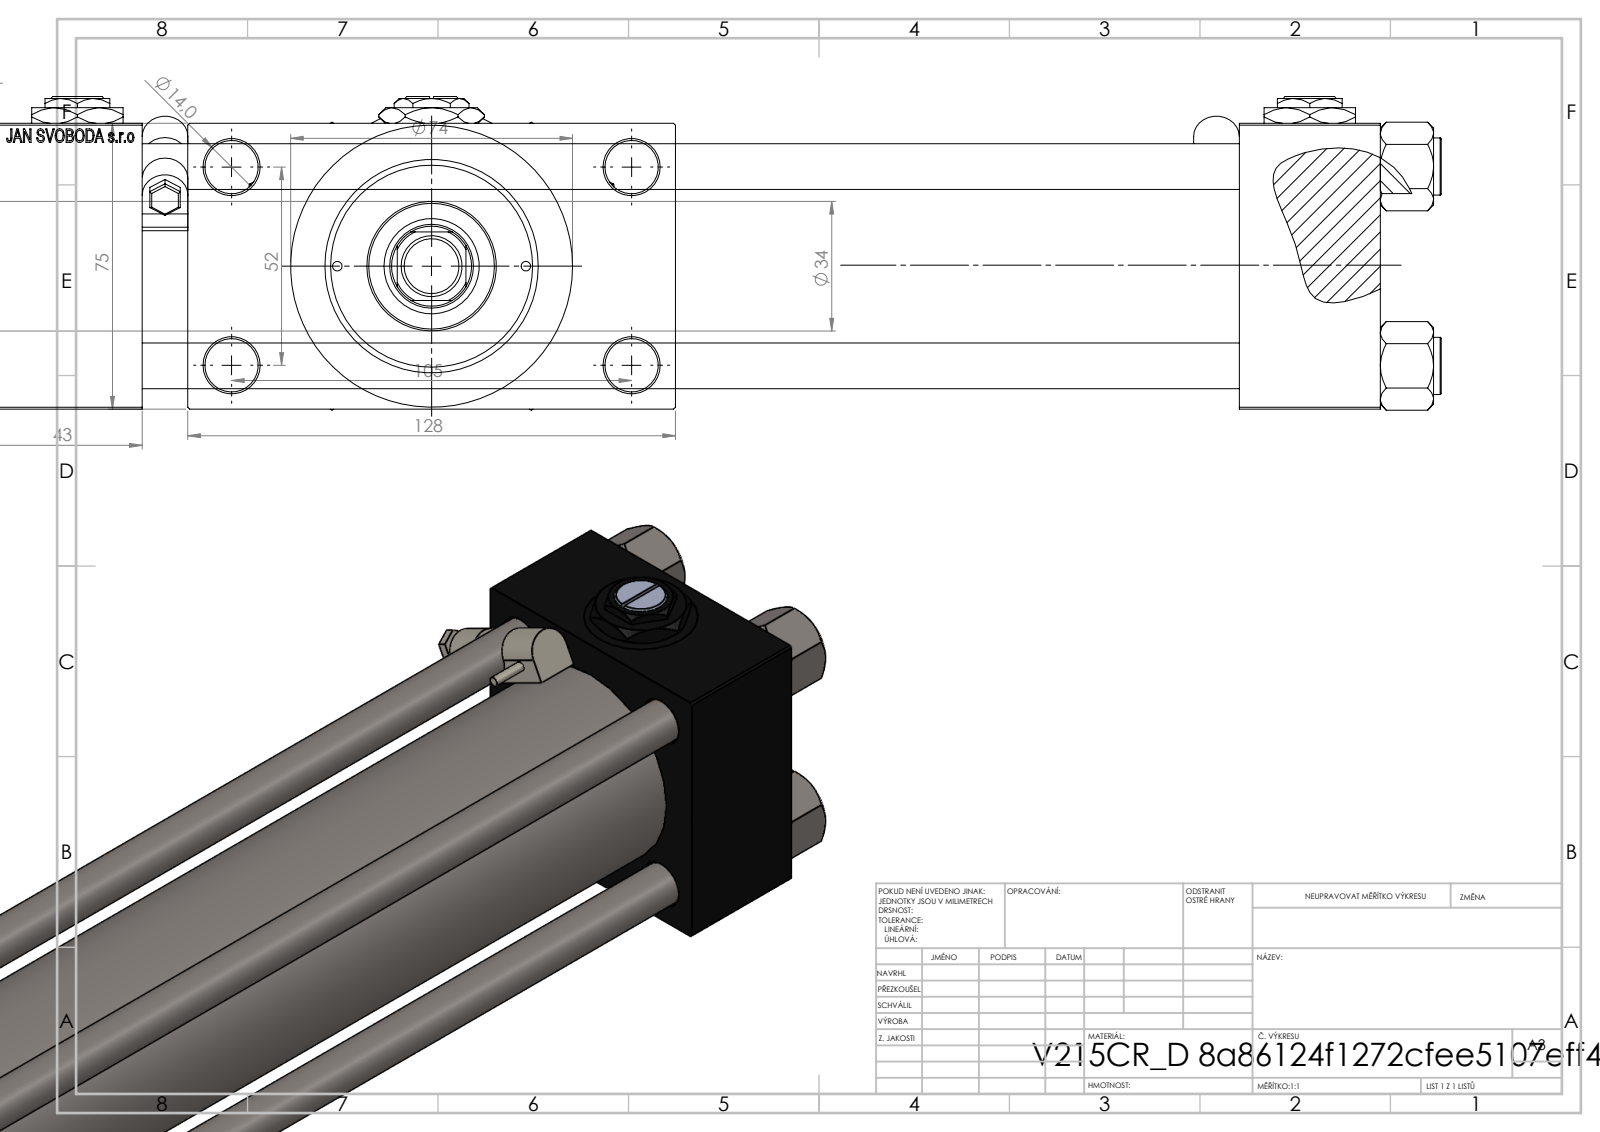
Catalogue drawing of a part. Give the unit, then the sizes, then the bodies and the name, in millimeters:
Units: millimetres
Overall size (bounding box): 447 × 128 × 82.27
Round holes (diameter × count): ⌀12 ×4, ⌀14 ×4, ⌀2.5 ×2, ⌀7 ×2, ⌀20.96 ×2, ⌀30 ×2, ⌀10.5 ×1, ⌀22 ×1, ⌀25 ×1, ⌀41 ×1, ⌀50 ×1, ⌀53 ×1
Round bosses / shafts (diameter × count): ⌀15 ×4, ⌀5 ×2, ⌀2.5 ×2, ⌀74 ×1, ⌀56 ×1, ⌀34 ×1, ⌀16 ×1, ⌀14 ×1
Partial cylindrical surfaces — rounded edges, fillets, slot ends (radius × count): R0.5 ×12, R6 ×4, R10.5 ×1
Main face-to-face distances: 75, 288, 37, 325, 26.5, 101.5, 368, 331, 43, 16
Hole centre spacings: 26.19, 26.35, 36.98, 38.03, 52.3, 57.22, 58.43, 58.59
Volume: 1 120 000 mm³ · Surface area: 302 325 mm²
Bodies: 16 solids, 1291 faces (587 planar, 136 cylindrical, 568 other)
Part name (STEP PRODUCT): V215_VC_A; ROD_END_AH; V215CR_D_Body; V215CR_D_TYCINKA (+4 more)
STEP written by: SolidWorks 2019 (CONFIG_CONTROL_DESIGN)
